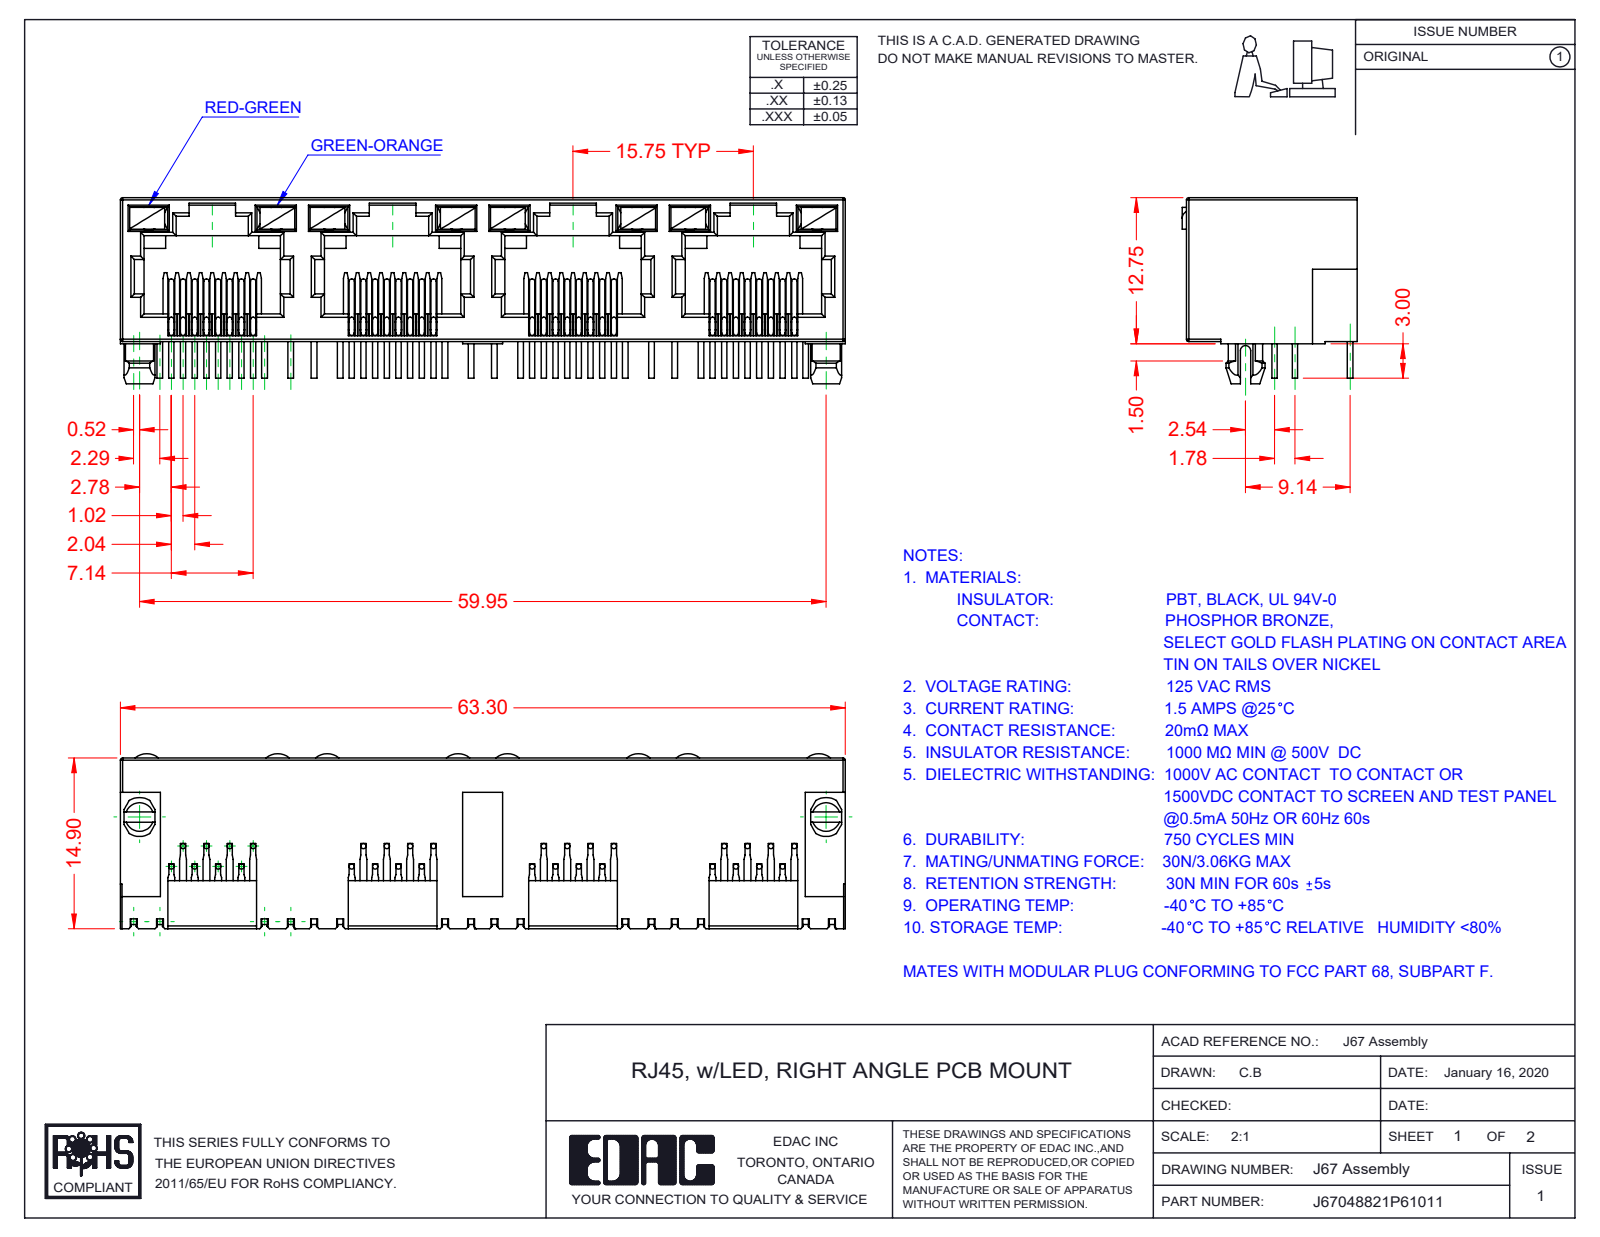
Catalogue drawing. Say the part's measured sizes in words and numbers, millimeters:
The part is named "67 LED LH_6-Red-Green; 67 LED RH_7-Green-Orange; 67 Contacts; 67 Insulator (+1 more)". Its 3-D file was written by "SolidWorks 2016 (CONFIG_CONTROL_DESIGN)". It is 41 solids with 2481 faces: 1781 planar, 492 cylindrical and 208 other. Overall it measures 63.3 by 16.25 by 15.28 millimeters. Its volume is 5 159 cubic millimeters and its surface area 11 573 square millimeters. Round bosses or shafts: 96 of diameter 0.46. Partial cylindrical surfaces (rounded edges, fillets, slot ends): 66 of radius 0.2, 29 of radius 0.3, 9 of radius 0.45, 8 of radius 1.55, 2 of radius 1.5, 2 of radius 1.7, 1 of radius 0.35, 1 of radius 1. The main face-to-face distances are 0.5, 12.55, 1.89, 0.89, 10, 15.75, 1, 1.39, 11, 11.89.
